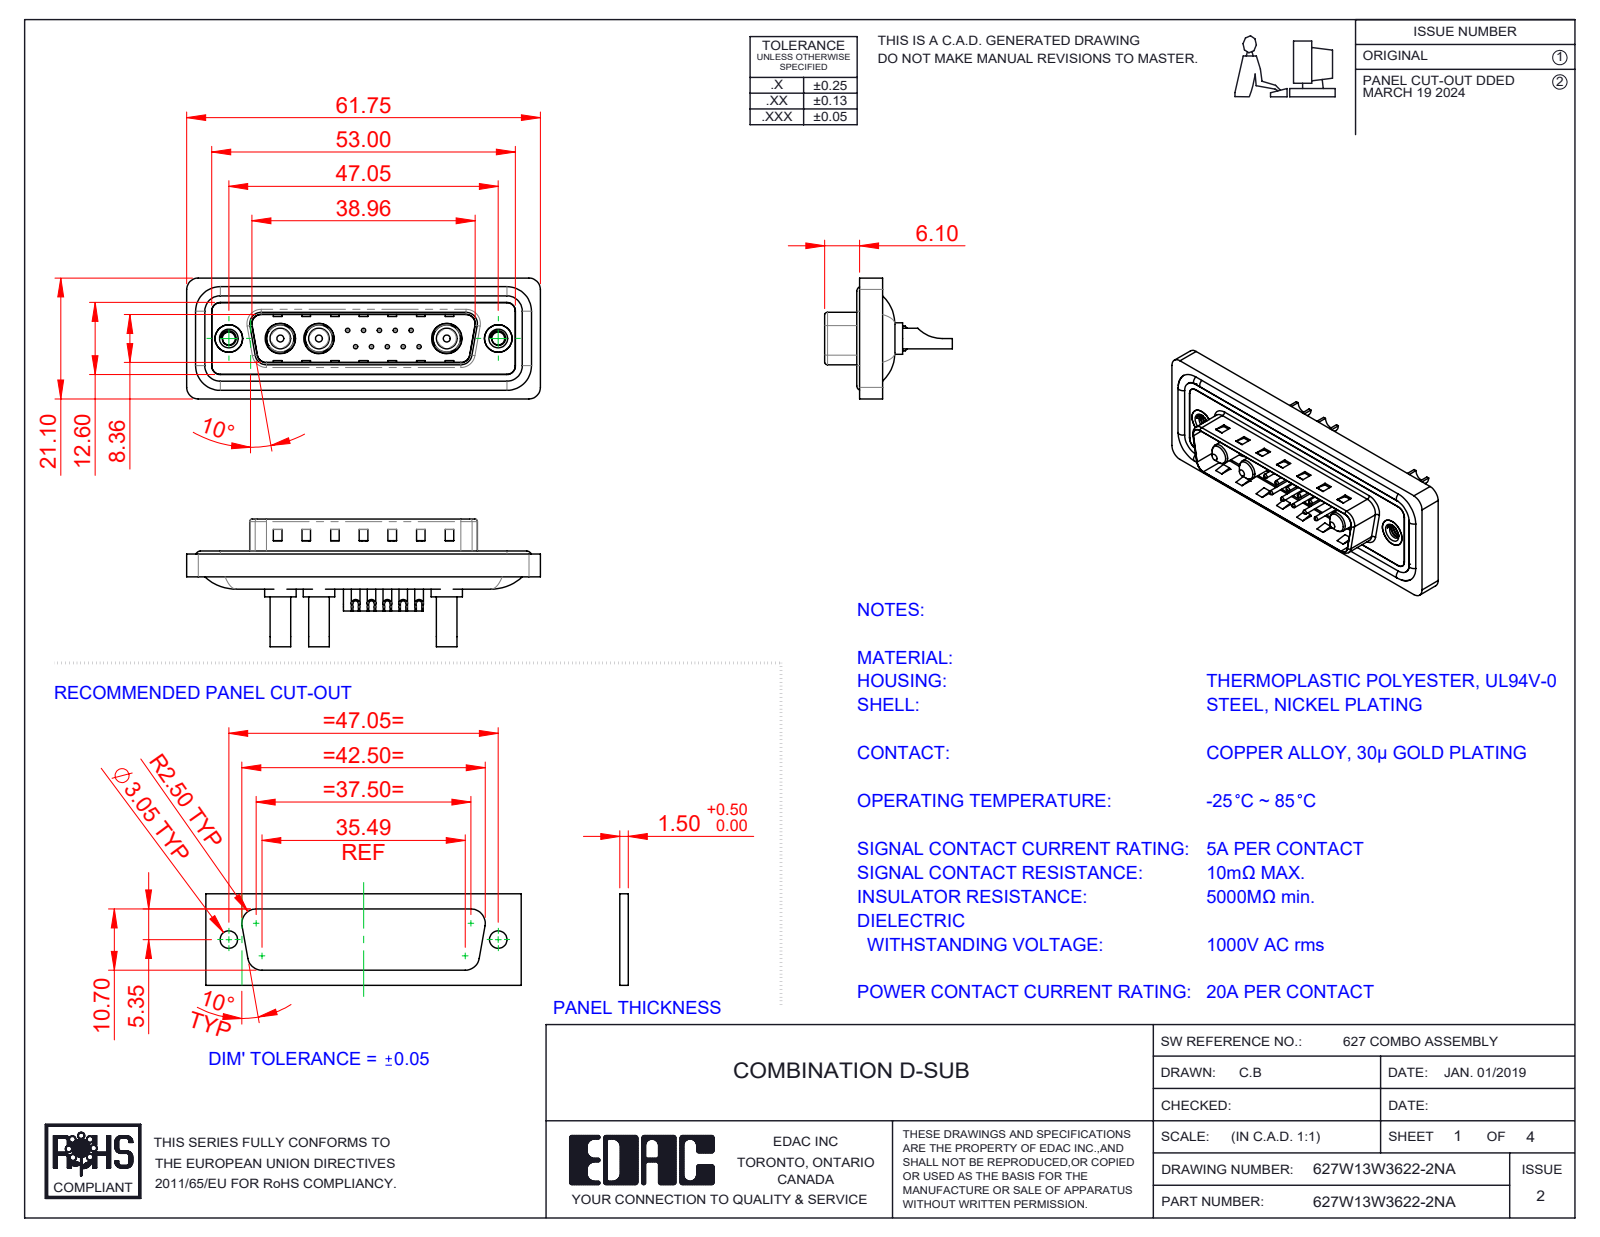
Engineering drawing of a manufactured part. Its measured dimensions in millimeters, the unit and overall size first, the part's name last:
Units: millimetres
Overall size (bounding box): 61.75 × 22.3 × 21.1
Round holes (diameter × count): ⌀0.75 ×10, ⌀1 ×10, ⌀1.6 ×10, ⌀2 ×10, ⌀2.7 ×3, ⌀4.85 ×3, ⌀5.3 ×3, ⌀2.26 ×2, ⌀4 ×2, ⌀4.8 ×2, ⌀5 ×2
Round bosses / shafts (diameter × count): ⌀1.5 ×10, ⌀1.6 ×4, ⌀5.5 ×3, ⌀5.2 ×3, ⌀4.75 ×3, ⌀3.75 ×3, ⌀3.6 ×3, ⌀4.9 ×2
Partial cylindrical surfaces — rounded edges, fillets, slot ends (radius × count): R1.5 ×22, R2 ×18, R0.5 ×8, R1.6 ×8, R1 ×6, R0.25 ×4, R0.6 ×4, R0.65 ×4
Main face-to-face distances: 0.4, 1.5, 1.1, 1.6, 0.5, 3.1, 2.9, 0.82, 9.58, 4.1
Hole centre spacings: 3.16, 2.77, 5.04, 5.54, 7.49, 5.03, 8.31, 10.11
Volume: 7 391 mm³ · Surface area: 12 199 mm²
Bodies: 23 solids, 989 faces (338 planar, 416 cylindrical, 235 other)
Part name (STEP PRODUCT): 627W13W3622-2NA; 627Combo Shell Front_25 Contacts; Power Pin_20A SC; 627Combo Contact Row 1_22 (+5 more)
STEP written by: SolidWorks 2023 (CONFIG_CONTROL_DESIGN)
